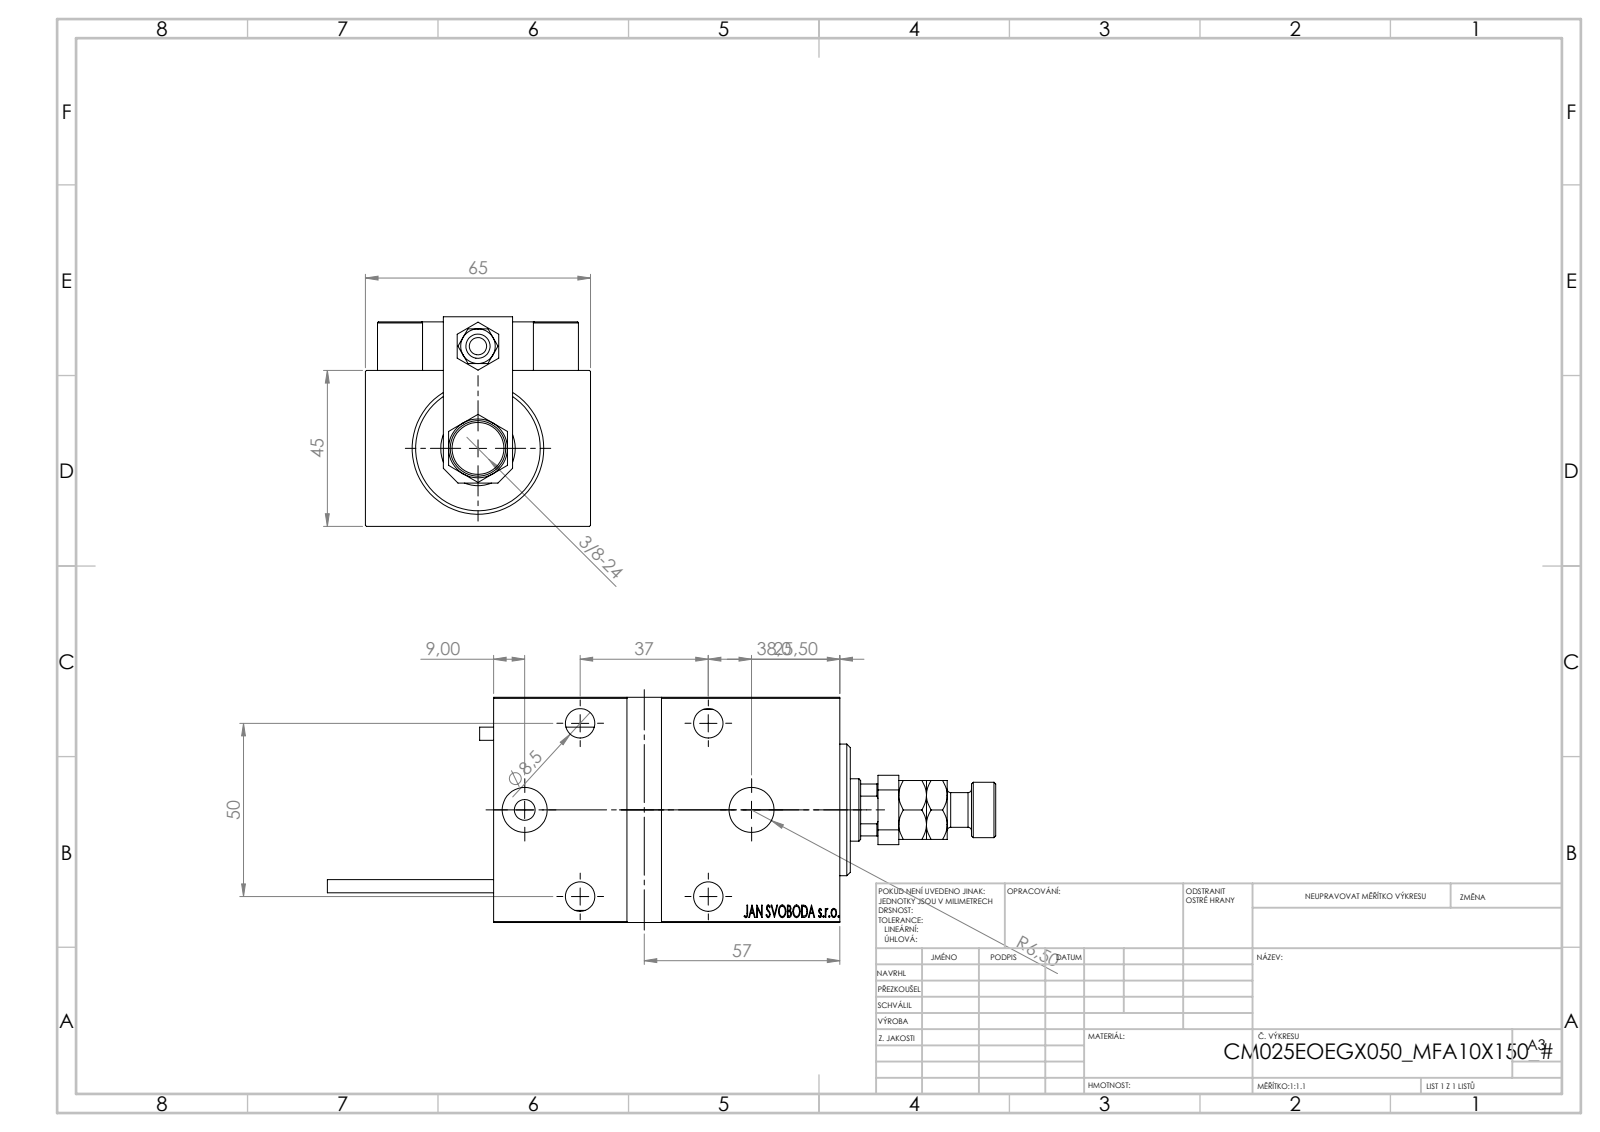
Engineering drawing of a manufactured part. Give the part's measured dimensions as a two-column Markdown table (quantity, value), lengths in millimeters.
| quantity | value |
| --- | --- |
| part name | SWITCH_X_FRONT_BACK; Block; X_Y_MFA; NUT_D12 (+7 more) |
| STEP written by | SolidWorks 2019 (CONFIG_CONTROL_DESIGN) |
| units | millimeters |
| bodies | 25 solids, 1338 faces (585 planar, 180 cylindrical, 573 other) |
| overall size | 193 × 65 × 60.5 |
| volume | 323 114 mm³ |
| surface area | 79 673 mm² |
| round holes (diameter × count) | 8 × 5, 8.5 × 5, 3.2 × 4, 4 × 4, 13.5 × 4, 5 × 2, 13 × 2, 7 × 1, 14.5 × 1, 18 × 1, 21.5 × 1, 25 × 1 |
| round bosses / shafts (diameter × count) | 5 × 2, 3.8 × 2, 38 × 1, 27 × 1, 16 × 1, 13 × 1, 11 × 1, 10 × 1 |
| partial cylindrical surfaces (radius × count) | 0.3 × 30, 3 × 2, 8.5 × 1 |
| main face-to-face distances | 45, 65, 14, 59, 6, 100, 111, 13, 10, 5 |
| hole center spacings | 40.31, 10.77, 11.37, 20, 21.03, 25, 27.95, 29.59 |
